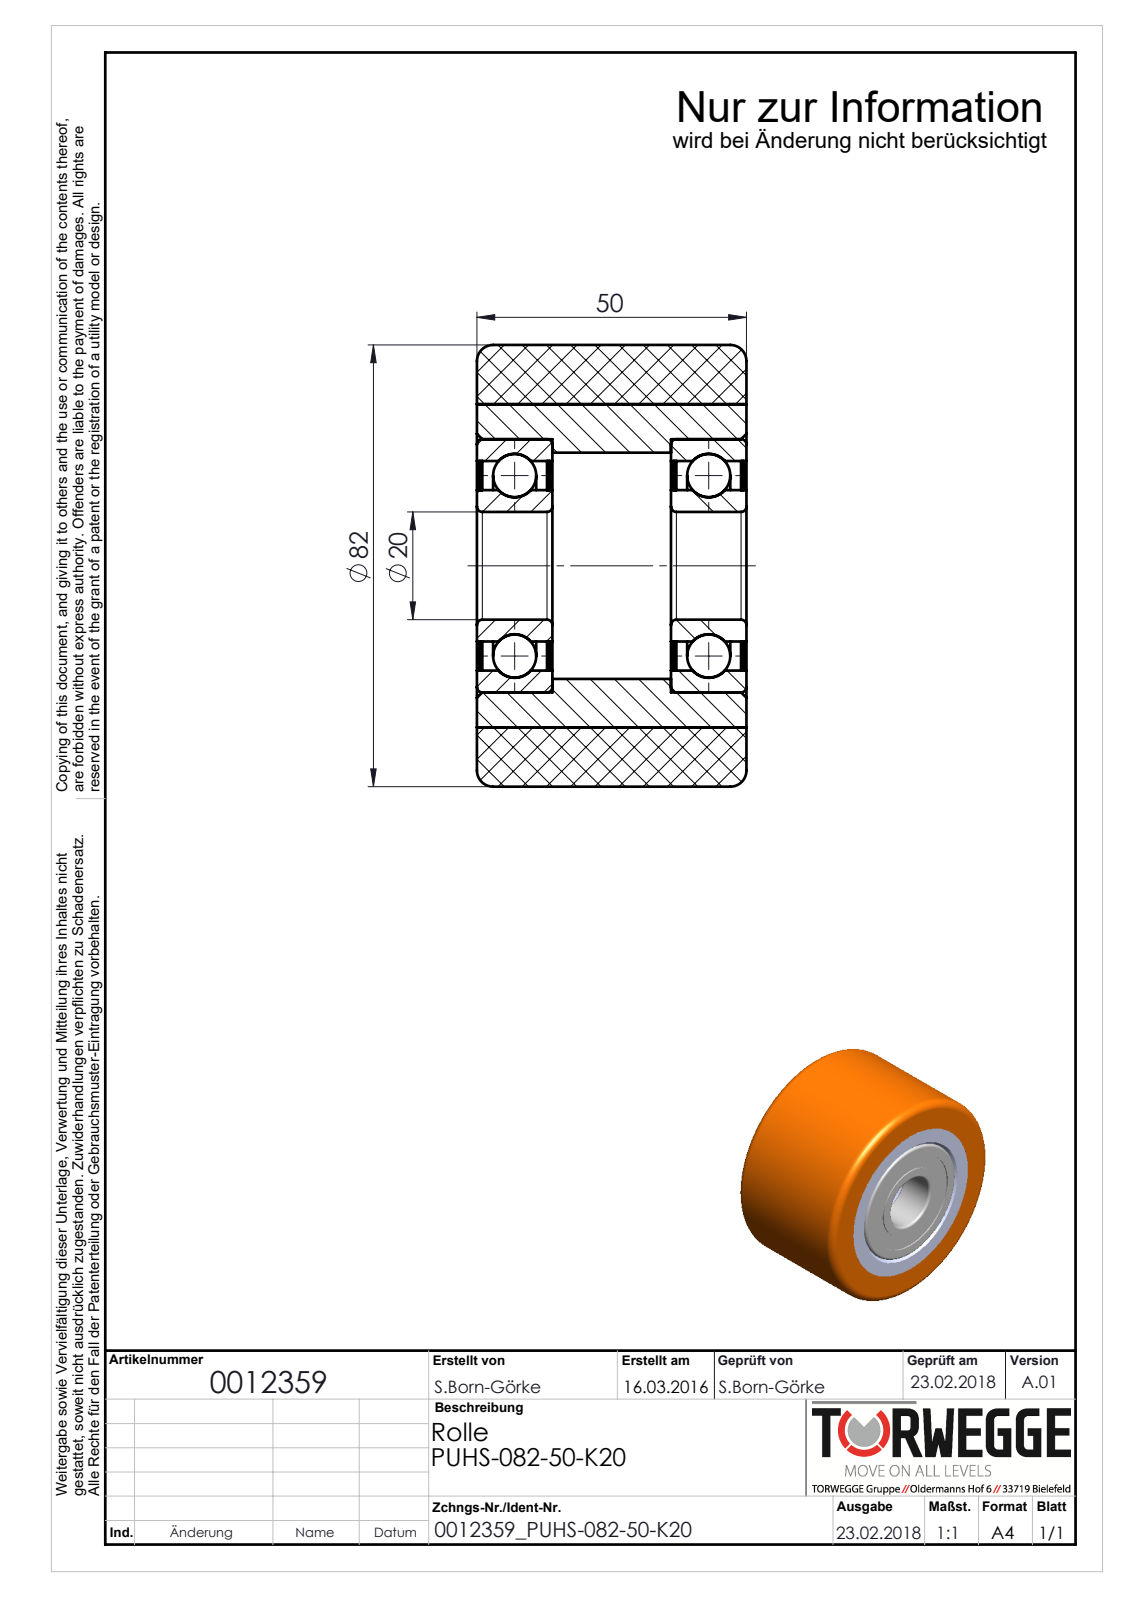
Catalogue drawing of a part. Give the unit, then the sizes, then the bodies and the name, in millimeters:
Units: millimetres
Overall size (bounding box): 82 × 82 × 50
Round holes (diameter × count): ⌀20 ×1, ⌀28.1 ×1, ⌀38.9 ×1, ⌀42 ×1, ⌀47 ×1, ⌀60 ×1
Round bosses / shafts (diameter × count): ⌀82 ×1
Main face-to-face distances: 0.5, 36, 13, 50, 1, 13.5, 36.5, 12.5, 35.5, 14
Volume: 216 748 mm³ · Surface area: 71 153 mm²
Bodies: 12 solids, 118 faces (22 planar, 52 cylindrical, 44 other)
Part name (STEP PRODUCT): 0012359_PUHS-082-50-K20
STEP written by: SolidWorks 2016 (AUTOMOTIVE_DESIGN)
